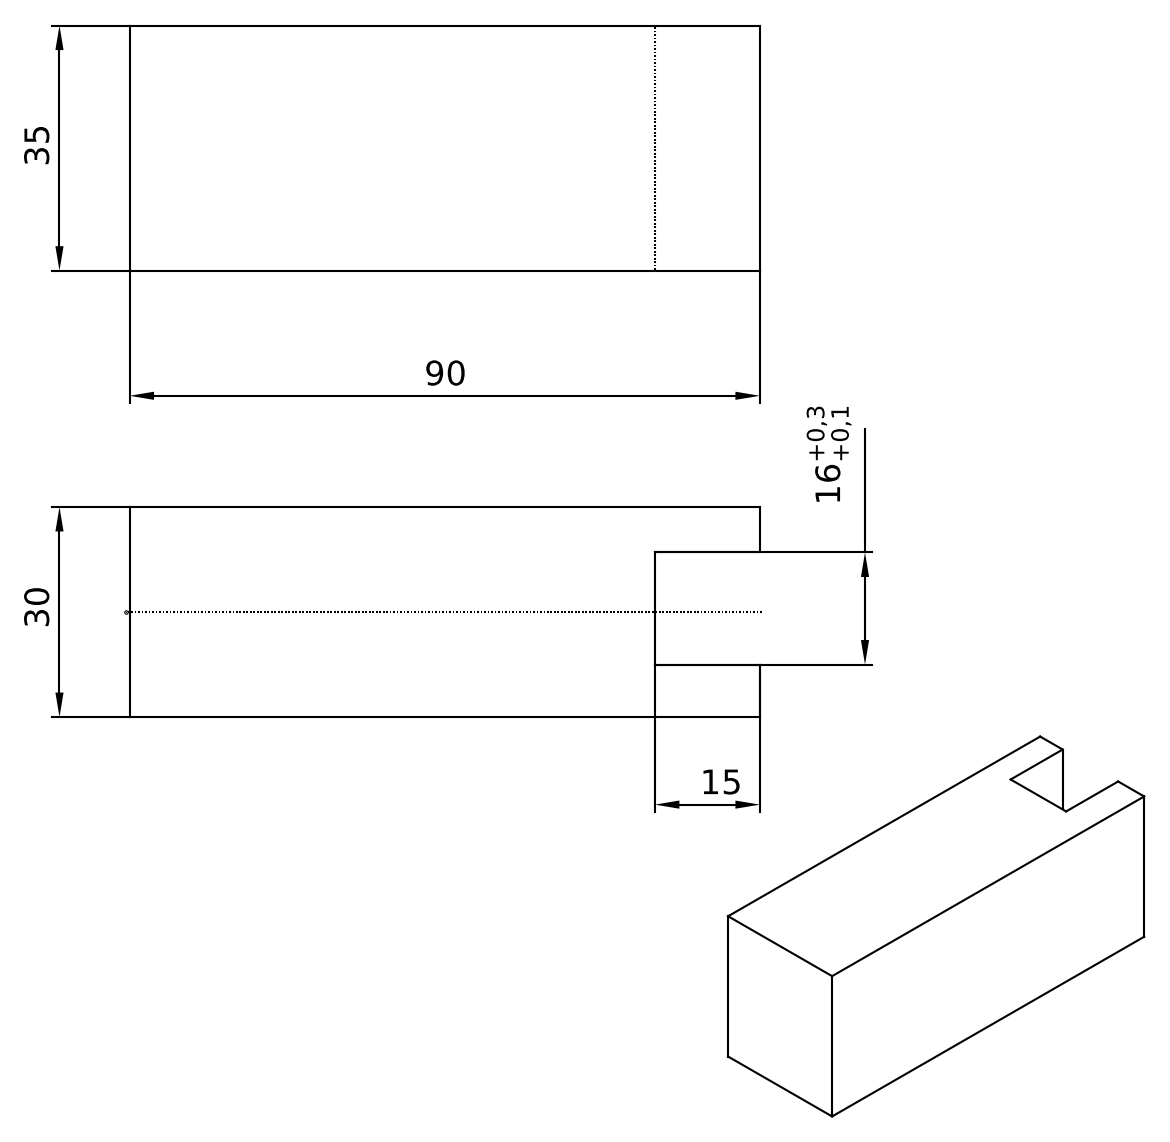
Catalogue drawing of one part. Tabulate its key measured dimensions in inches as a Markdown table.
| quantity | value |
| --- | --- |
| part name | 606-21E1 |
| STEP written by | Autodesk Inventor 8 (AUTOMOTIVE_DESIGN) |
| units | inches |
| bodies | 1 solid, 10 faces (10 planar, 0 cylindrical, 0 other) |
| overall size | 3.543 × 1.378 × 1.181 |
| volume | 5.254 in³ |
| surface area | 22.27 in² |
| main face-to-face distances | 1.181, 1.378, 2.953, 0.256, 0.886, 0.63, 0.925, 0.295, 3.543, 0.591 |
